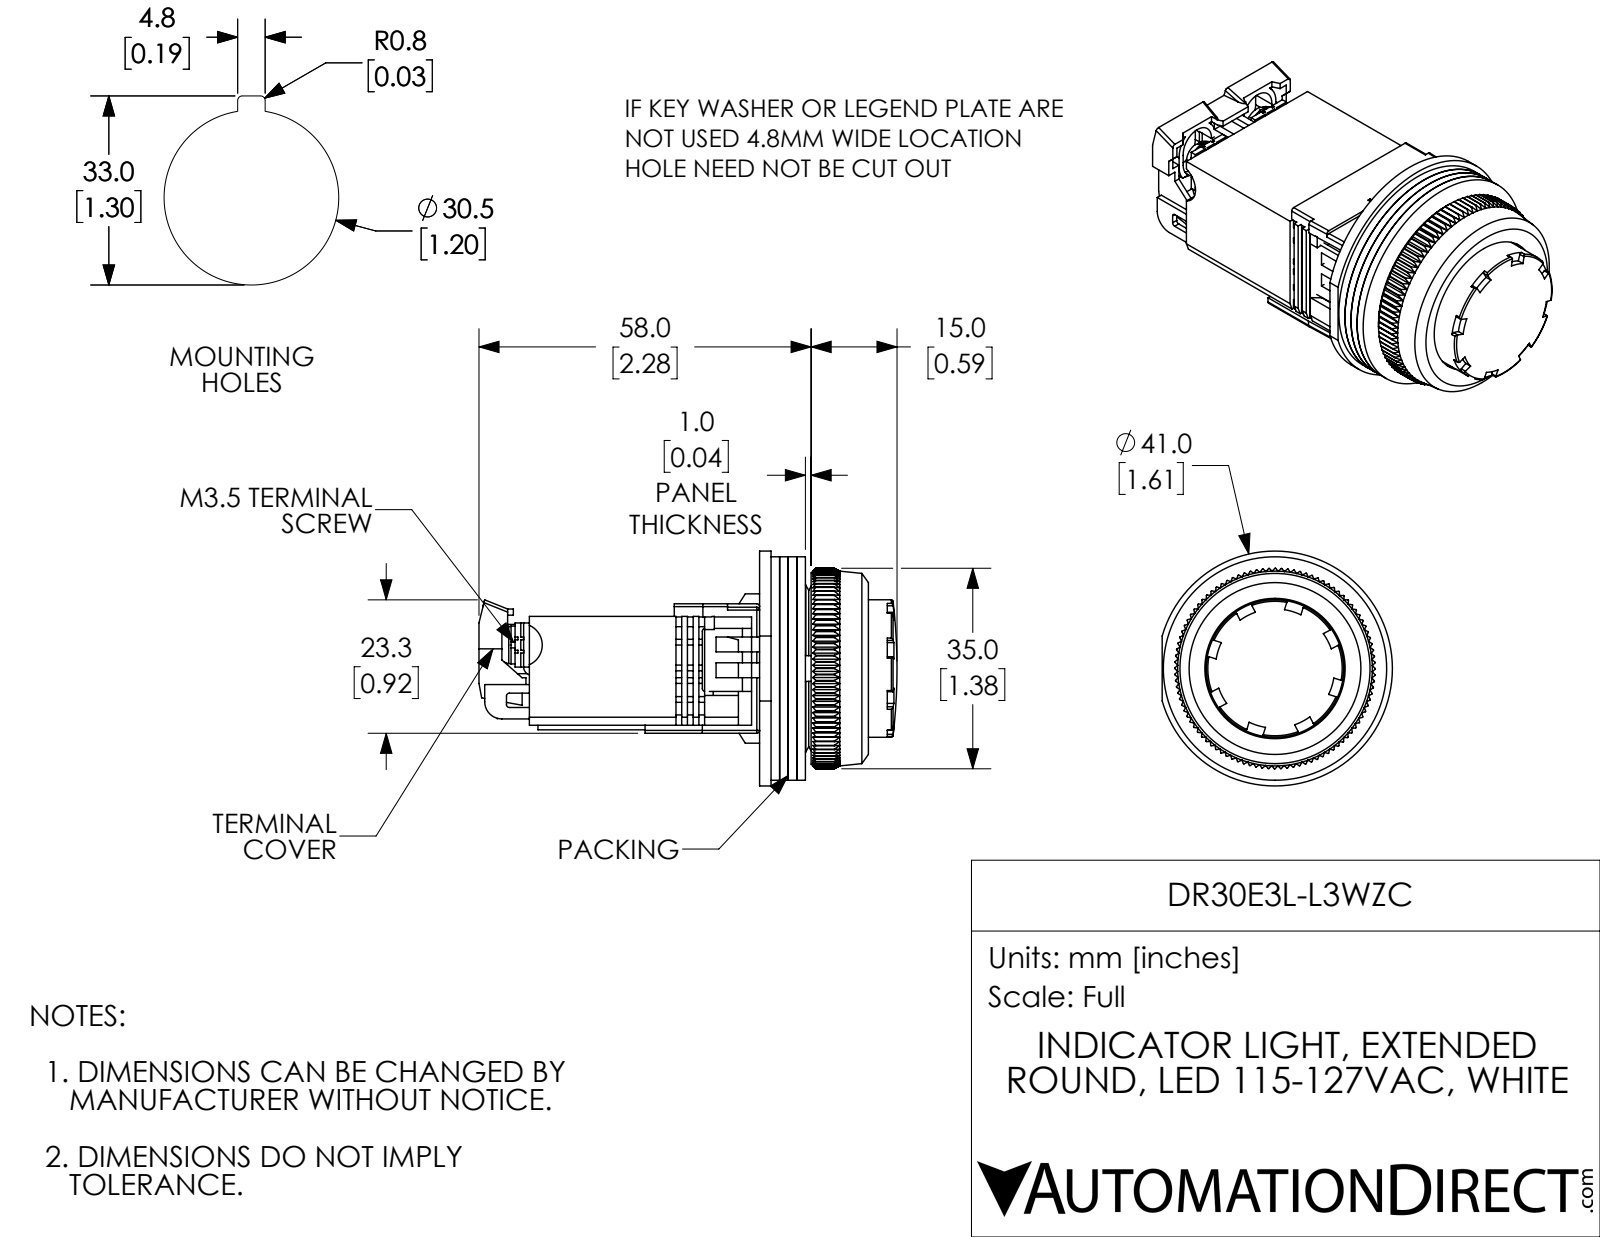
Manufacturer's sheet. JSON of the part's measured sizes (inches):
{"part_name": "DR30E3L-L3WZC", "step_written_by": "SolidWorks 2017 (AUTOMOTIVE_DESIGN)", "units": "inches", "bodies": {"solids": 19, "faces": 1662, "planar": 1058, "cylindrical": 340, "other": 264}, "overall_size": [2.874, 1.614, 1.583], "volume_in3": 2.318, "surface_area_in2": 53.06, "round_holes": [[0.118, 2], [0.138, 2], [0.142, 2], [0.465, 1], [0.563, 1], [0.72, 1], [0.787, 1], [0.866, 1], [0.965, 1], [1.122, 1], [1.173, 1], [1.181, 1]], "round_bosses_or_shafts": [[0.26, 2], [0.063, 2], [1.614, 1], [1.535, 1], [1.16, 1], [0.945, 1], [0.858, 1], [0.819, 1]], "partial_cylinders_radius": [[0.02, 24], [0.012, 16], [0.059, 9], [0.138, 2], [0.177, 2], [0.016, 1], [0.055, 1], [0.118, 1]], "face_to_face_distances": [0.059, 0.118, 0.039, 0.177, 0.197, 0.079, 0.256, 0.315, 0.748, 0.138], "hole_center_spacings": [0.333, 0.02, 0.324, 0.583, 0.583]}
